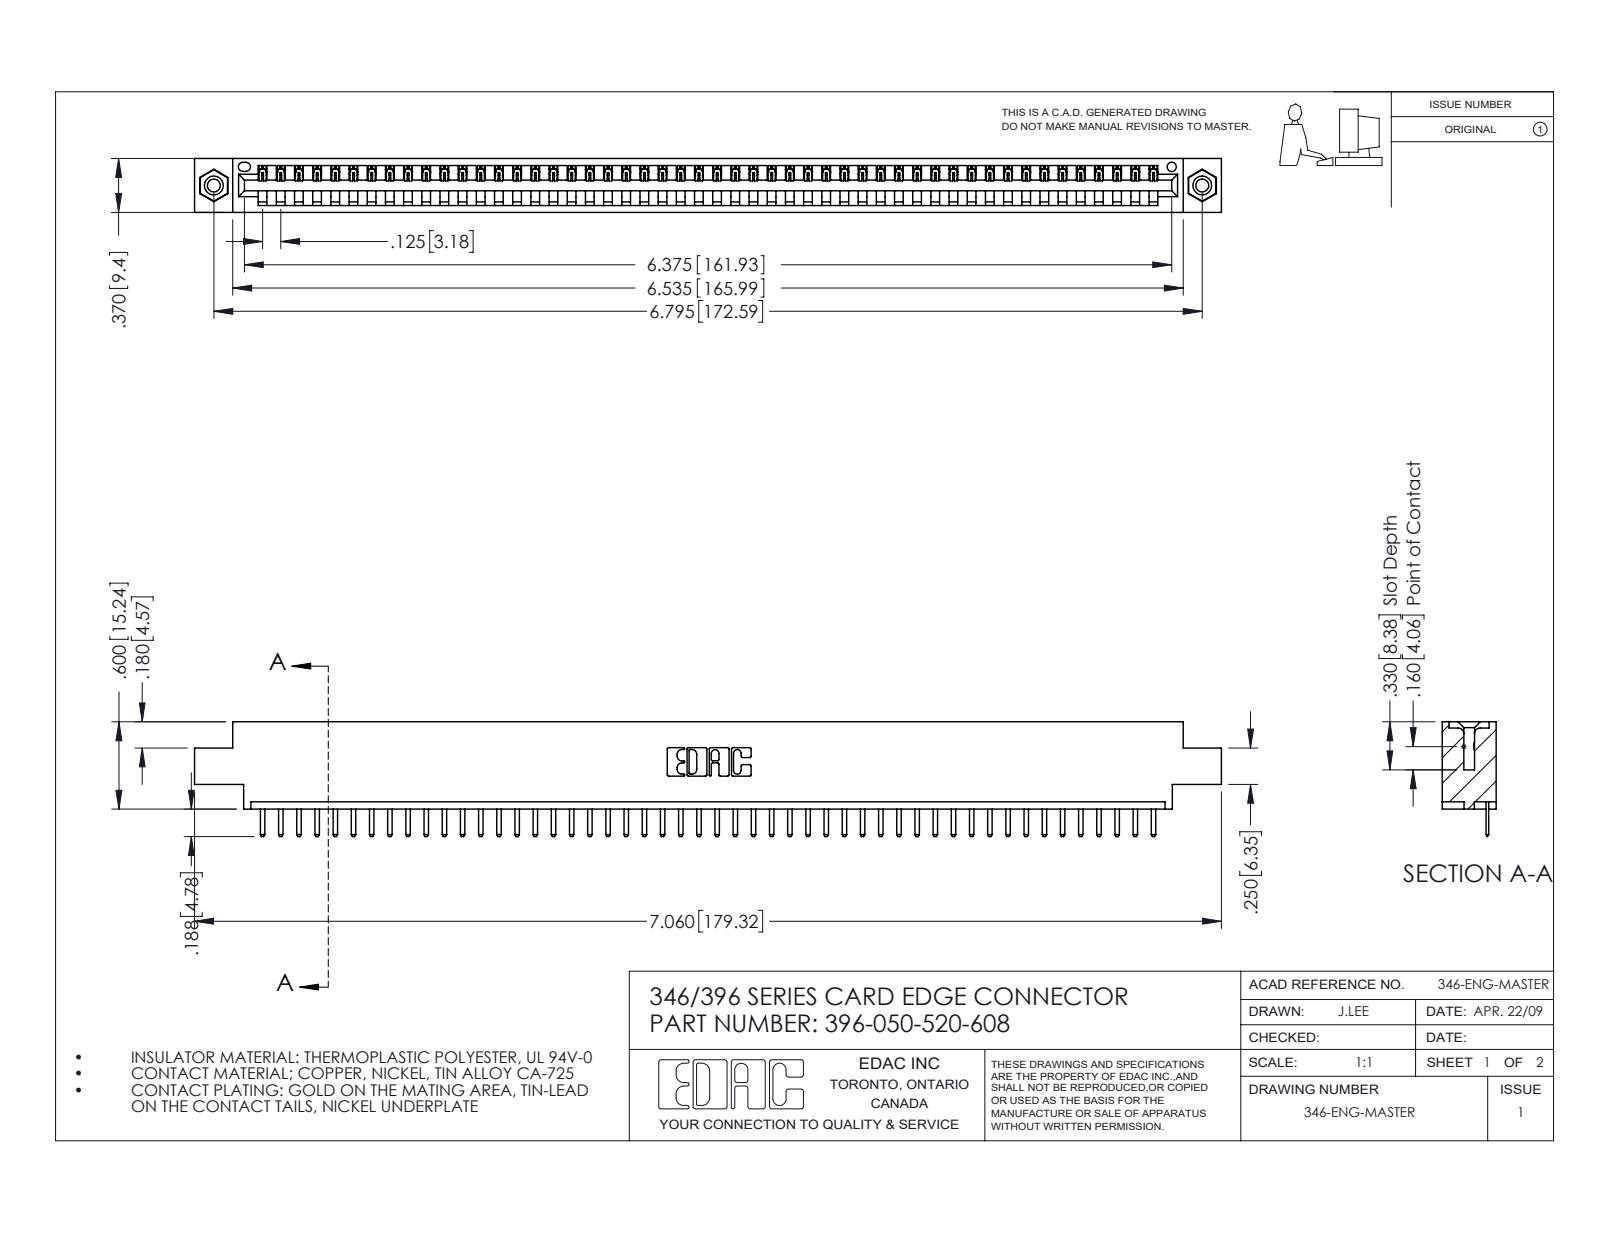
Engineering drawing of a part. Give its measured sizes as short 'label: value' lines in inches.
name: 396-050-520-608; 345-250-001_345-250-003-102; 345-292-001_345-293-120; 346 Part_0.170 Offset - 0.156 Dia-TI
written by: SolidWorks 2016 (CONFIG_CONTROL_DESIGN)
unit: in
bodies: 53 solids, 3286 faces (2212 planar, 1058 cylindrical, 16 other)
size: 7.06 × 0.788 × 0.37
volume: 1.032 in³; area: 32.44 in²
holes: 2× ⌀0.089, 2× ⌀0.125, 2× ⌀0.156, 1× ⌀0.064
bosses: 2× ⌀0.155
rounds: 102× R0.01, 100× R0.006, 22× R0.01, 6× R0.007, 6× R0.031, 3× R0.026, 2× R0.031, 2× R0.04
face distances: 0.048, 0.322, 0.37, 0.25, 0.222, 0.148, 0.1, 0.174, 0.072, 0.298
hole spacings: 0.246, 6.586, 6.795
